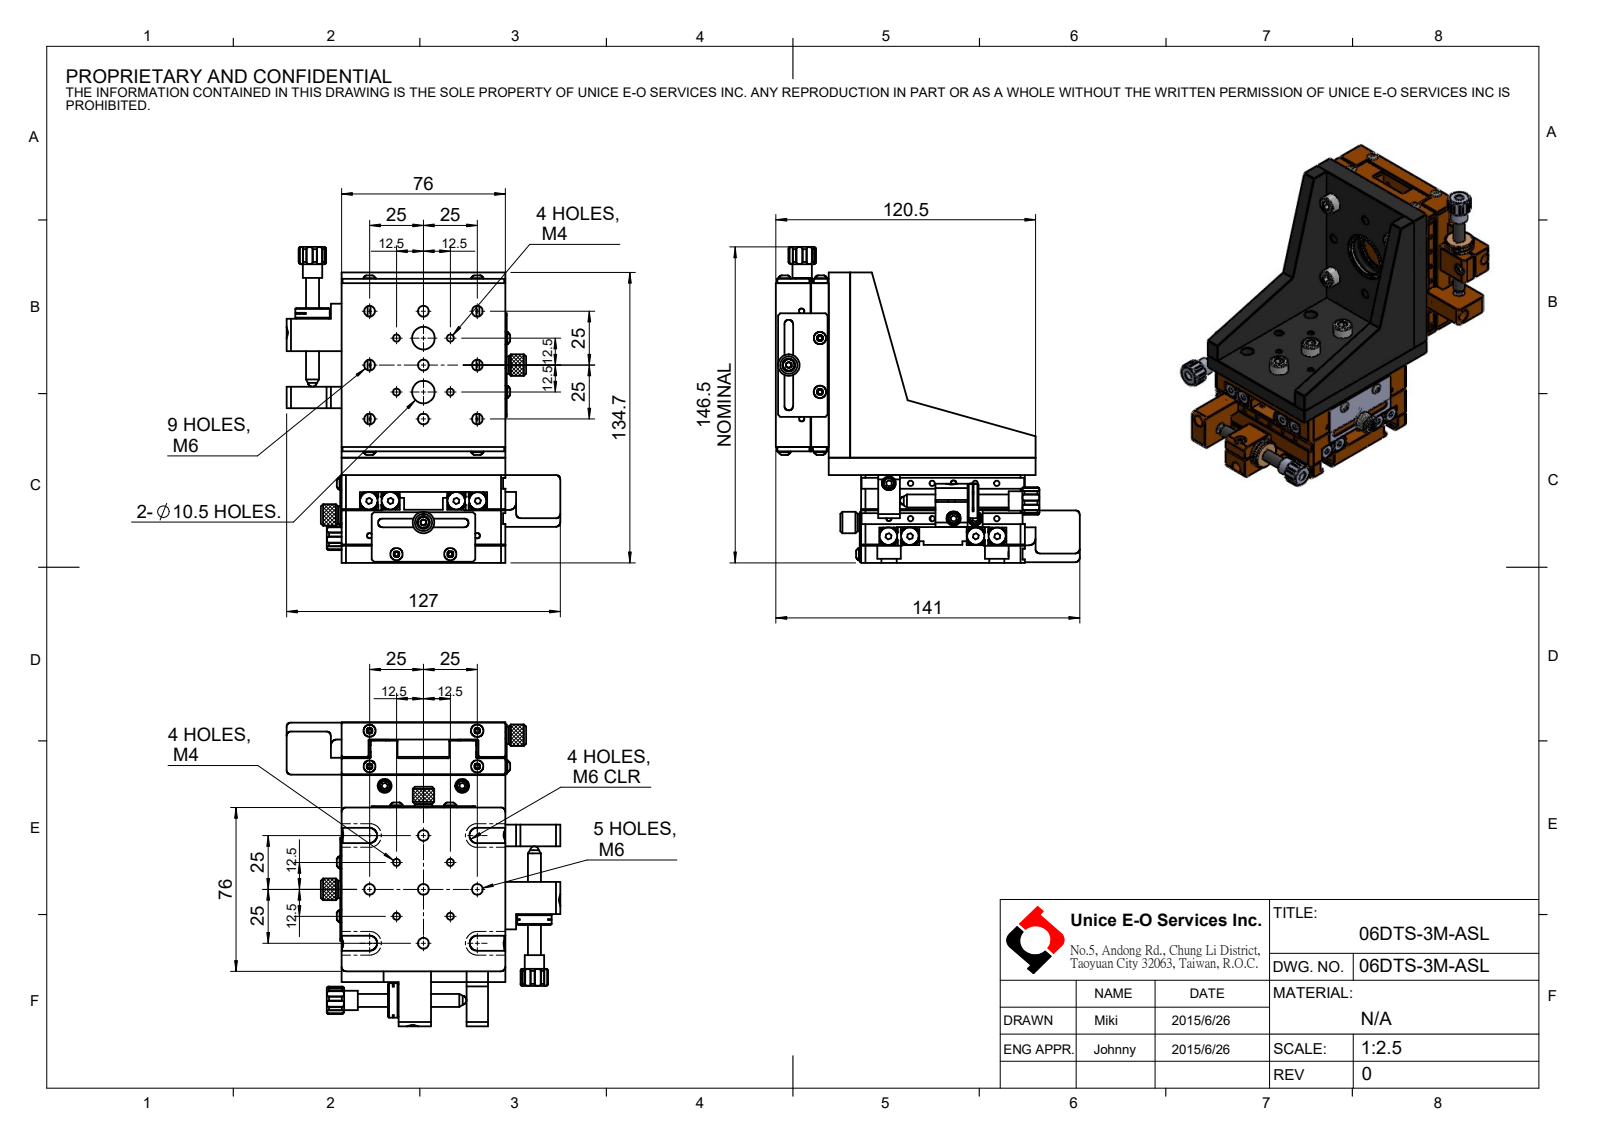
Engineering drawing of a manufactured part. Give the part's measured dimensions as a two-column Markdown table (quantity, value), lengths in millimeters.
| quantity | value |
| --- | --- |
| part name | 06DTS-3M-ASL |
| STEP written by | SolidWorks 2016 (CONFIG_CONTROL_DESIGN) |
| units | millimeters |
| bodies | 128 solids, 4362 faces (1439 planar, 1589 cylindrical, 1334 other) |
| overall size | 146.5 × 141 × 127 |
| volume | 513 173 mm³ |
| surface area | 247 251 mm² |
| round holes (diameter × count) | 2.5 × 121, 3.5 × 30, 6 × 30, 3.3 × 27, 3.4 × 22, 6.5 × 22, 4.5 × 18, 5 × 17, 7 × 11, 3.2 × 6, 3 × 3, 4 × 3 |
| round bosses / shafts (diameter × count) | 3 × 34, 5.5 × 25, 6 × 16, 5.7 × 12, 8 × 11, 4 × 11, 10 × 10, 16 × 3 |
| partial cylindrical surfaces (radius × count) | 0.3 × 48, 0.5 × 32, 2 × 28, 2.75 × 24, 5.5 × 4, 3 × 3, 6.35 × 3 |
| main face-to-face distances | 16.4, 8.2, 8, 8.5, 7.9, 8.3, 76, 5, 16.1, 8.1 |
| hole center spacings | 25, 10, 50, 20, 30, 17.68, 39.53, 12.66 |
